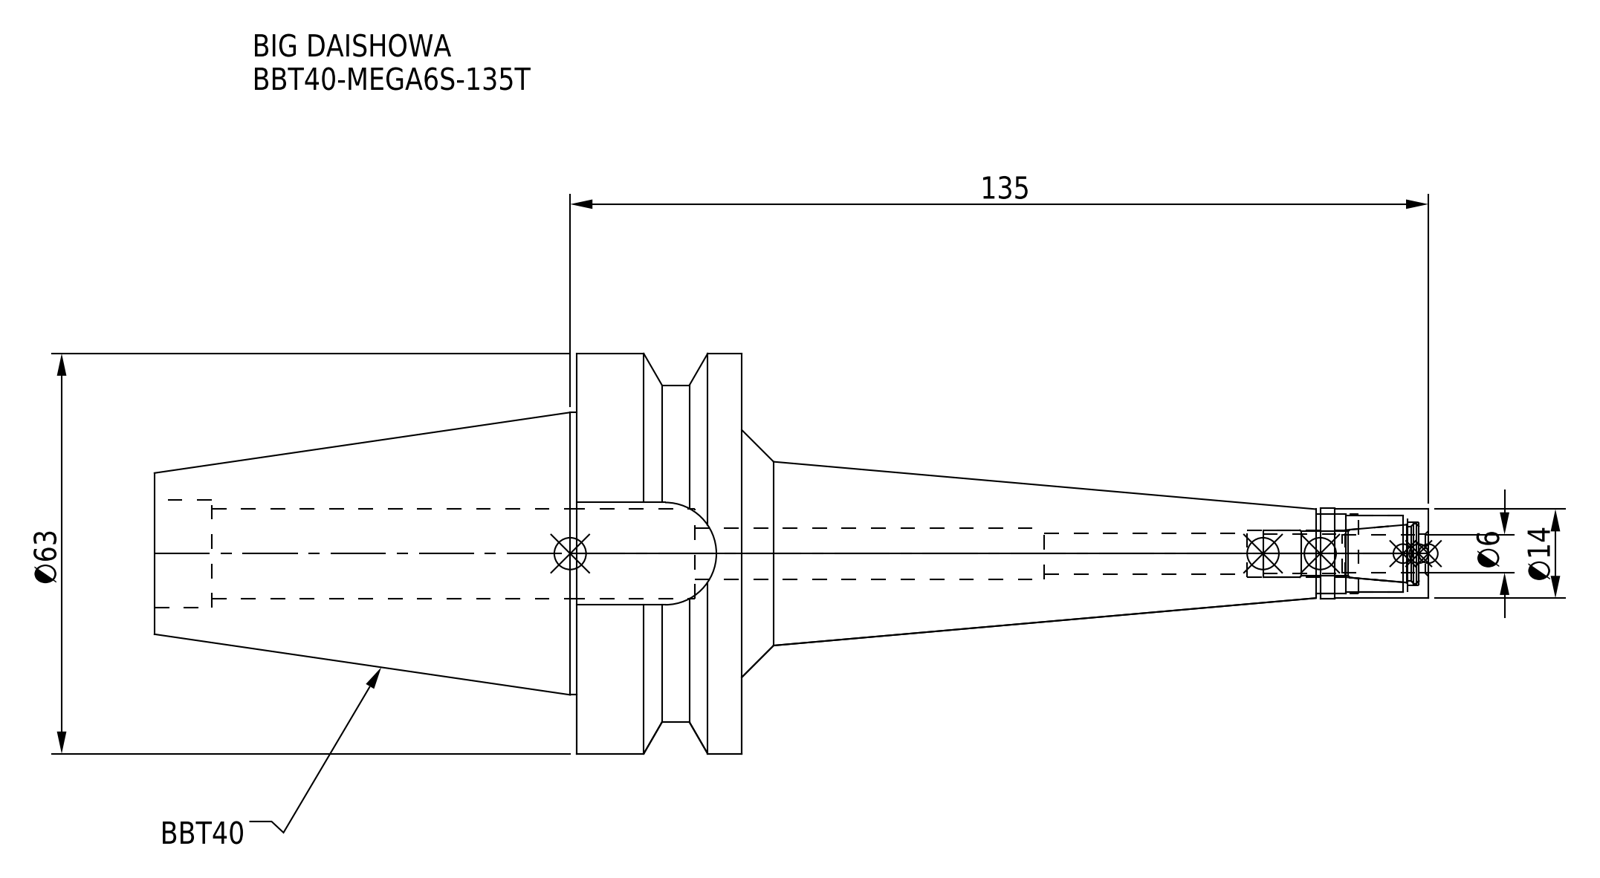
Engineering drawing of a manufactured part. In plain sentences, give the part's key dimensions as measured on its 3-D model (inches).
The part is named "BBT40-MEGA6S-135T_1.stp; MGN6S_1.stp; BBT40-MEGA6S-135T-060.stp; DXF_TEMP_ASSY_ASM_4_ASM.stp (+3 more)". Its 3-D file was written by "SolidWorks 2019 (CONFIG_CONTROL_DESIGN)". It is 2 solids with 74 faces: 22 planar, 38 cylindrical and 14 other. Overall it measures 7.89 by 2.48 by 2.48 inches. Its volume is 9.499 cubic inches and its surface area 50.92 square inches. Round holes: 1 of diameter 0.24, 1 of diameter 0.252, 1 of diameter 0.291, 1 of diameter 0.315, 1 of diameter 0.394, 1 of diameter 0.472, 1 of diameter 0.492, 1 of diameter 0.559, 1 of diameter 0.669. Round bosses or shafts: 1 of diameter 2.48, 1 of diameter 2.087, 1 of diameter 1.75, 1 of diameter 0.563, 1 of diameter 0.551. Partial cylindrical surfaces (rounded edges, fillets, slot ends): 1 of radius 0.317. The main face-to-face distances are 1.024, 1.772, 3.638, 2.614, 0.634, 4.252, 5.276, 7.89, 4.543, 0.291.
